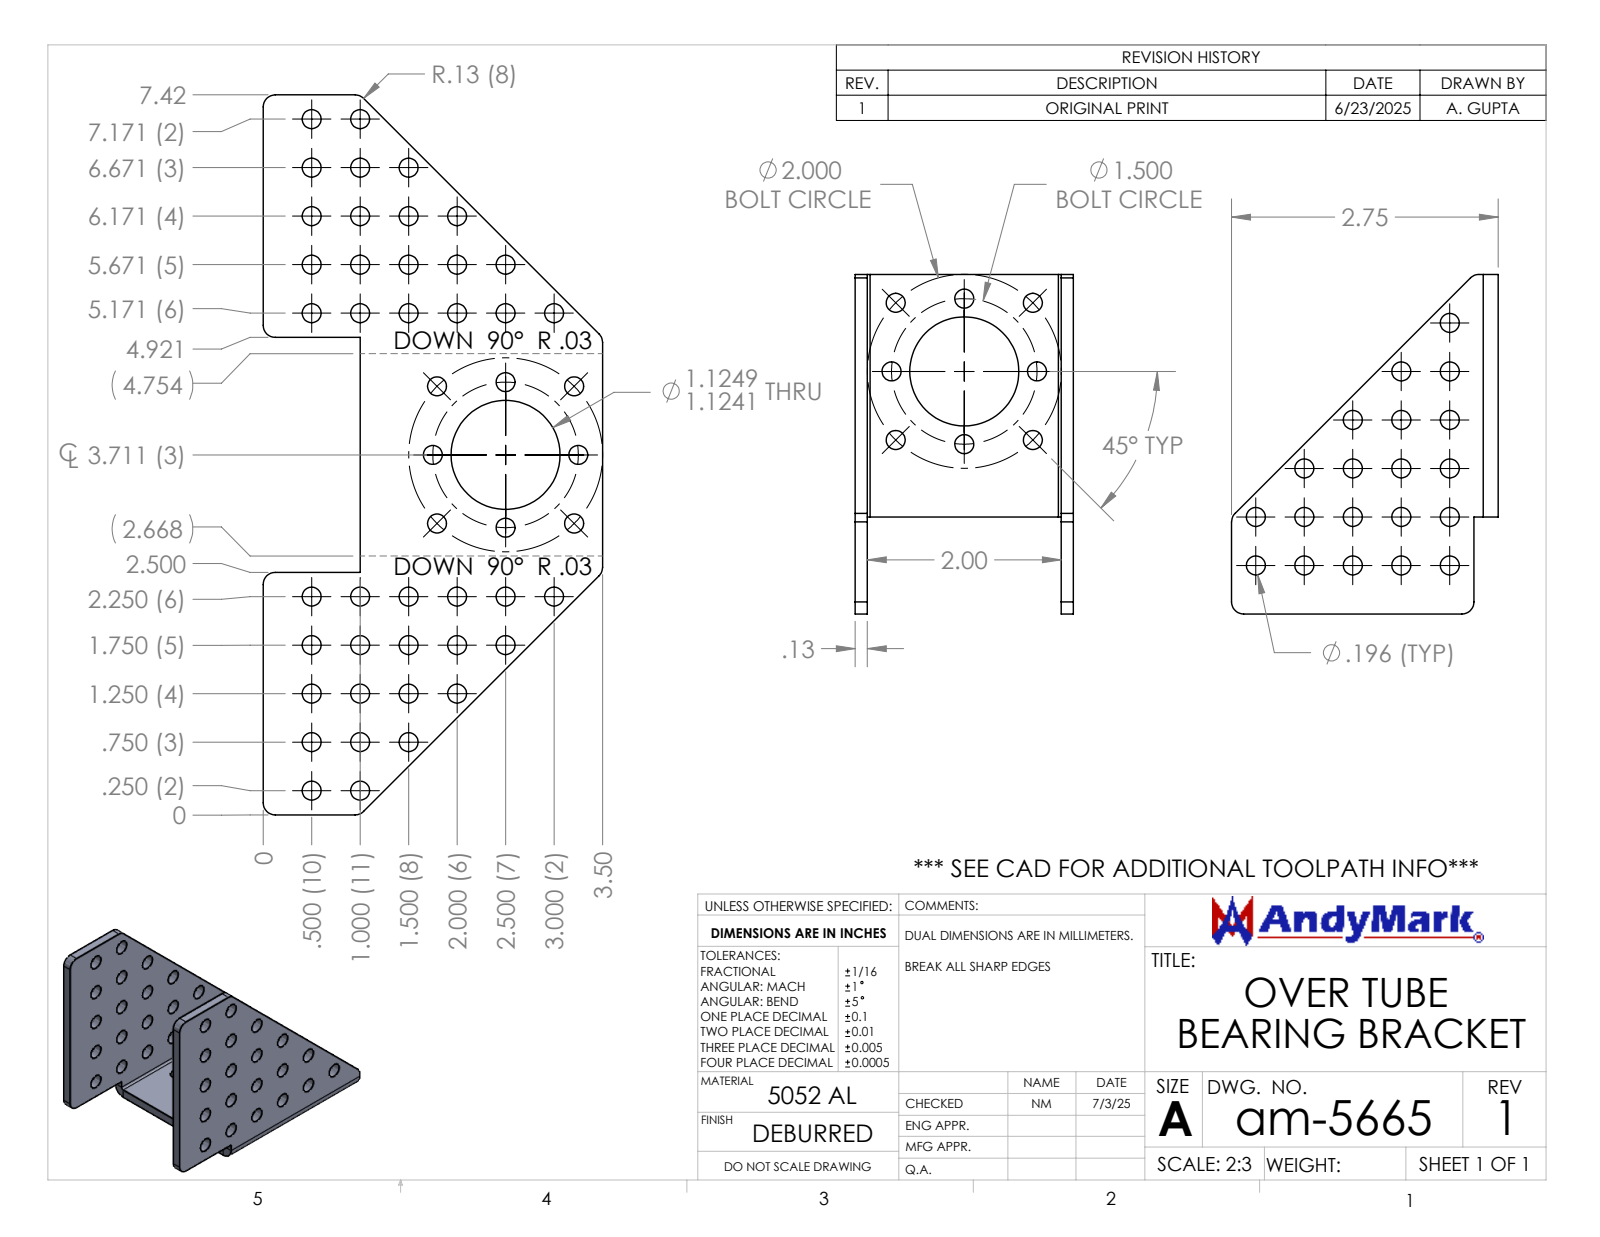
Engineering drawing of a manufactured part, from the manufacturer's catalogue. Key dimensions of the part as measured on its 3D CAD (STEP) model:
Part name (STEP PRODUCT): am-5665 Over Tube Bearing Bracket
STEP written by: SolidWorks 2024 (AUTOMOTIVE_DESIGN)
Units: inches
Bodies: 1 solid, 134 faces (24 planar, 110 cylindrical, 0 other)
Overall size (bounding box): 3.5 × 2.75 × 2.25
Volume: 1.856 in³ · Surface area: 36.42 in²
Round holes (diameter × count): ⌀0.196 ×28, ⌀1.124 ×1
Partial cylindrical surfaces — rounded edges, fillets, slot ends (radius × count): R0.125 ×6, R0.029 ×2, R0.154 ×2
Main face-to-face distances: 0.125, 2.125, 2, 2.25, 0.125, 2.5, 1, 3.5, 0.25, 2.75
Hole centre spacings: 1.118, 0.5, 0.707, 1, 1.581, 1.414, 1.5, 1.803
